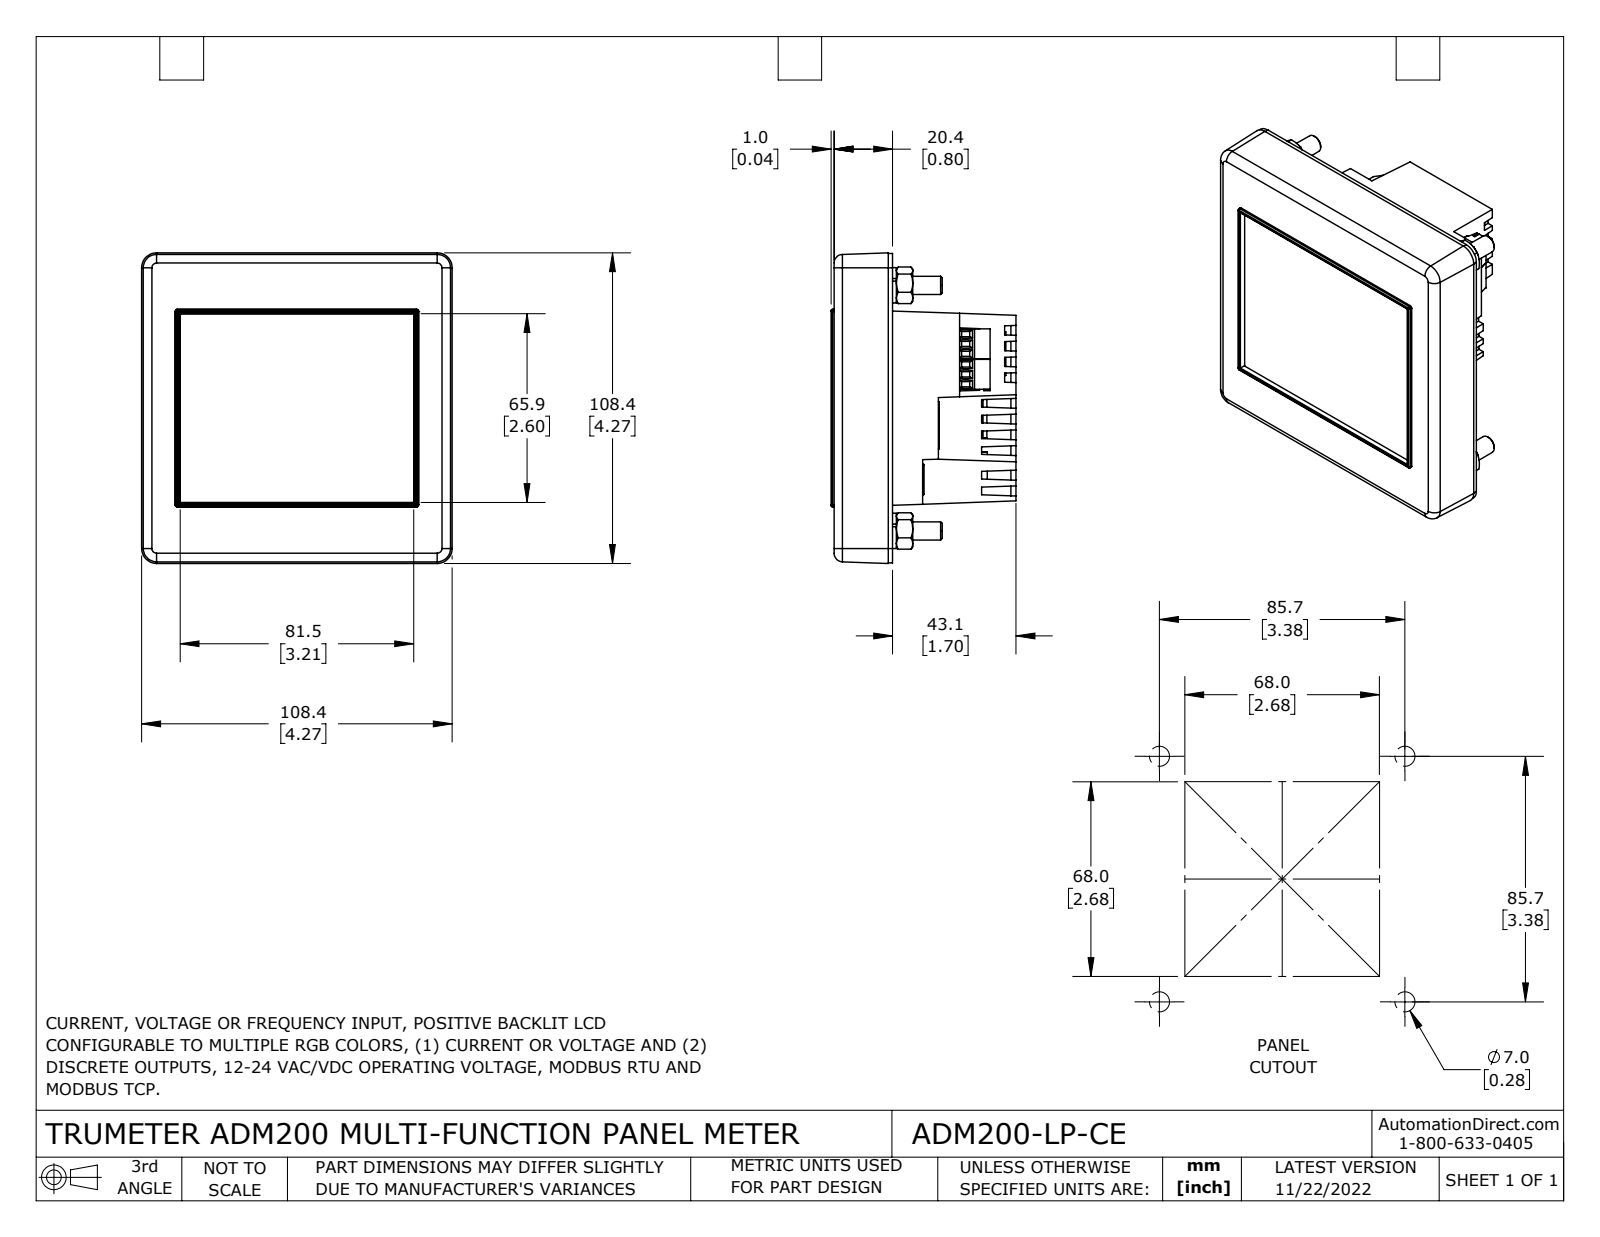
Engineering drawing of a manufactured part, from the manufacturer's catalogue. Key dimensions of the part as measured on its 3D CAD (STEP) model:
Part name (STEP PRODUCT): ADM200-LP-CE
STEP written by: SolidWorks 2021 (CONFIG_CONTROL_DESIGN)
Units: inches
Bodies: 23 solids, 2059 faces (1384 planar, 290 cylindrical, 385 other)
Overall size (bounding box): 4.269 × 4.269 × 2.541
Volume: 7.808 in³ · Surface area: 190.8 in²
Round holes (diameter × count): ⌀0.071 ×9, ⌀0.114 ×6, ⌀0.118 ×5, ⌀0.213 ×4, ⌀0.25 ×4, ⌀0.26 ×4, ⌀0.295 ×4, ⌀0.154 ×2
Round bosses / shafts (diameter × count): ⌀0.039 ×5, ⌀0.487 ×4, ⌀0.438 ×4, ⌀0.024 ×4, ⌀0.079 ×2
Partial cylindrical surfaces — rounded edges, fillets, slot ends (radius × count): R0.006 ×32, R0.02 ×30, R0.039 ×7, R0.016 ×4, R0.03 ×4, R0.118 ×4, R0.197 ×4, R0.004 ×2
Main face-to-face distances: 0.031, 0.635, 0.11, 0.073, 0.059, 0.079, 0.694, 3.395, 3.468, 0.047
Hole centre spacings: 0.709, 3.228, 0.136, 0.293, 0.986, 1.417, 2.126, 2.399
